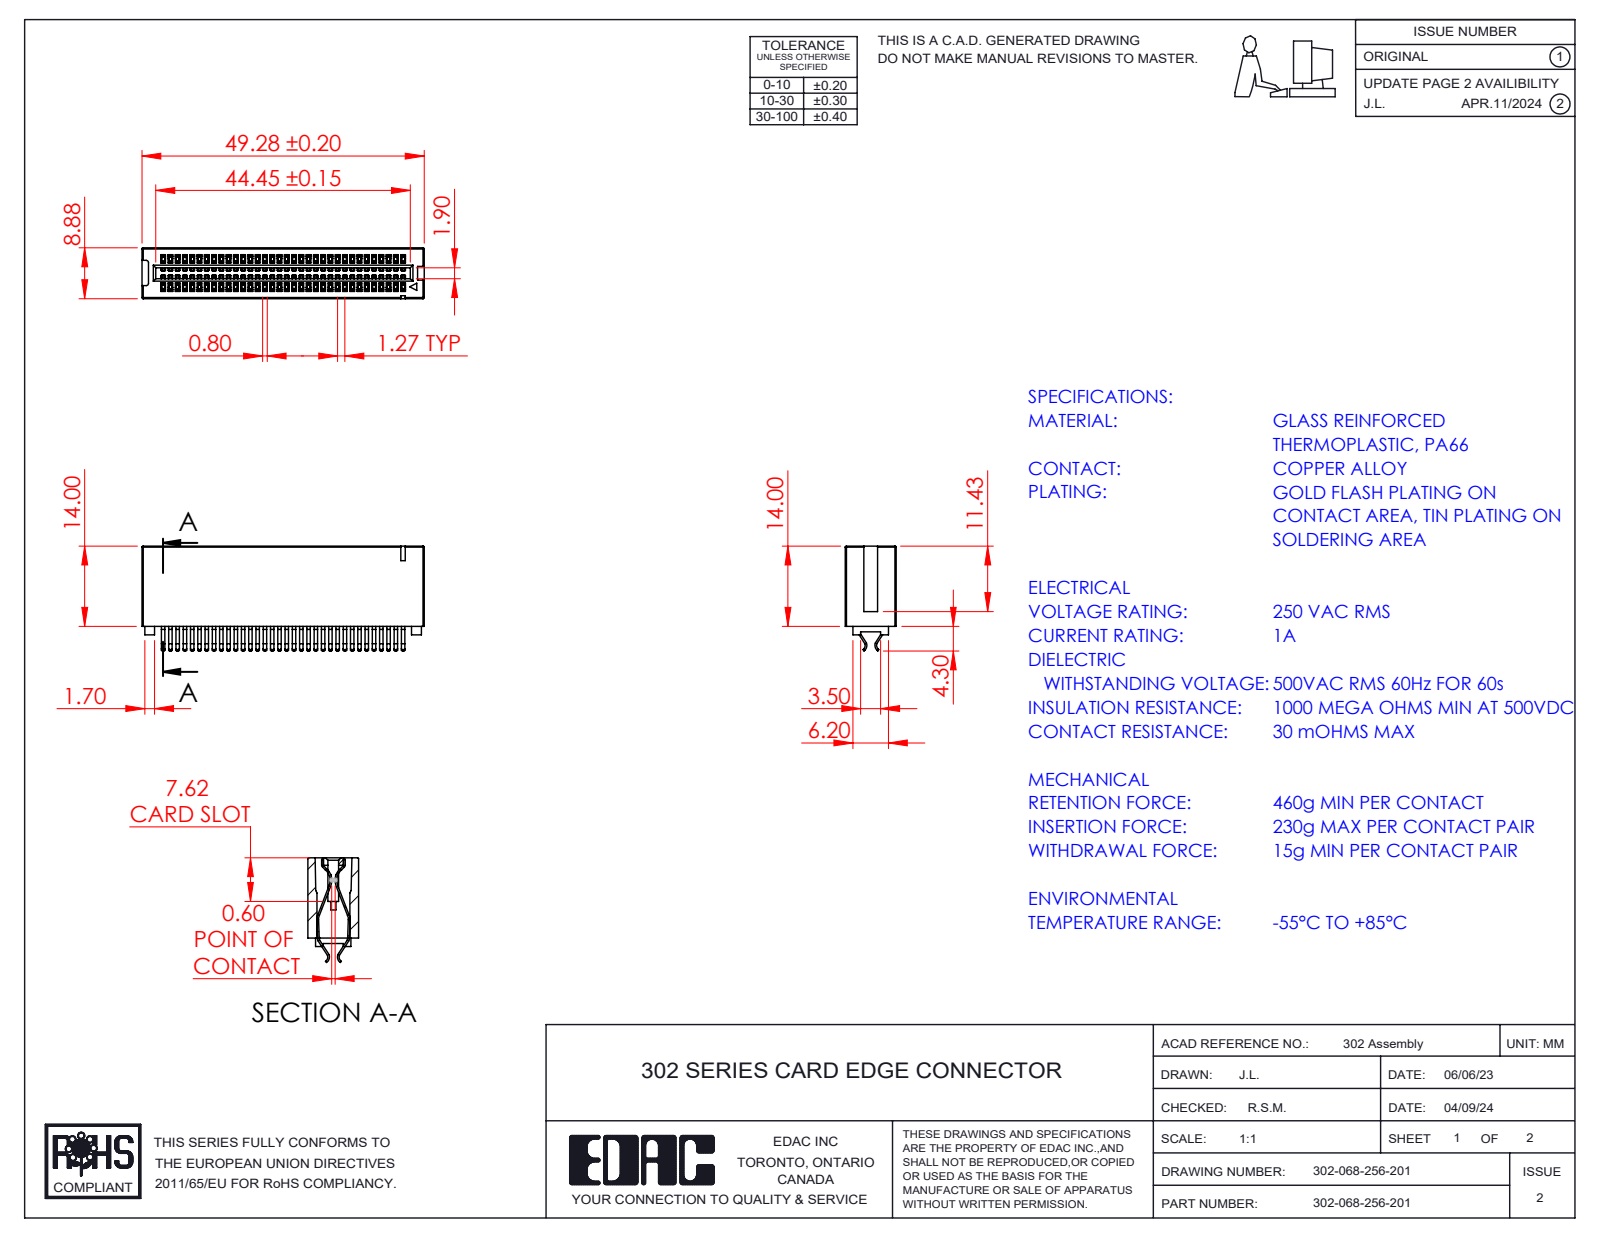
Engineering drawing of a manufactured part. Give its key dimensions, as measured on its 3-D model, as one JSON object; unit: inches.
{"part_name": "HSG_Vertical HSG; 302-068-256-201; Contact_302-290-X56", "step_written_by": "SolidWorks 2023 (CONFIG_CONTROL_DESIGN)", "units": "inches", "bodies": {"solids": 69, "faces": 3296, "planar": 2191, "cylindrical": 1101, "other": 4}, "overall_size": [1.94, 0.72, 0.35], "volume_in3": 0.235, "surface_area_in2": 16.37, "partial_cylinders_radius": [[0.008, 212], [0.004, 2], [0.016, 2], [0.016, 2], [0.037, 2], [0.041, 2], [0.048, 2], [0.049, 2]], "face_to_face_distances": [0.05, 0.1, 0.35, 0.15, 0.031, 0.2, 0.019, 0.081, 0.131, 0.25]}
